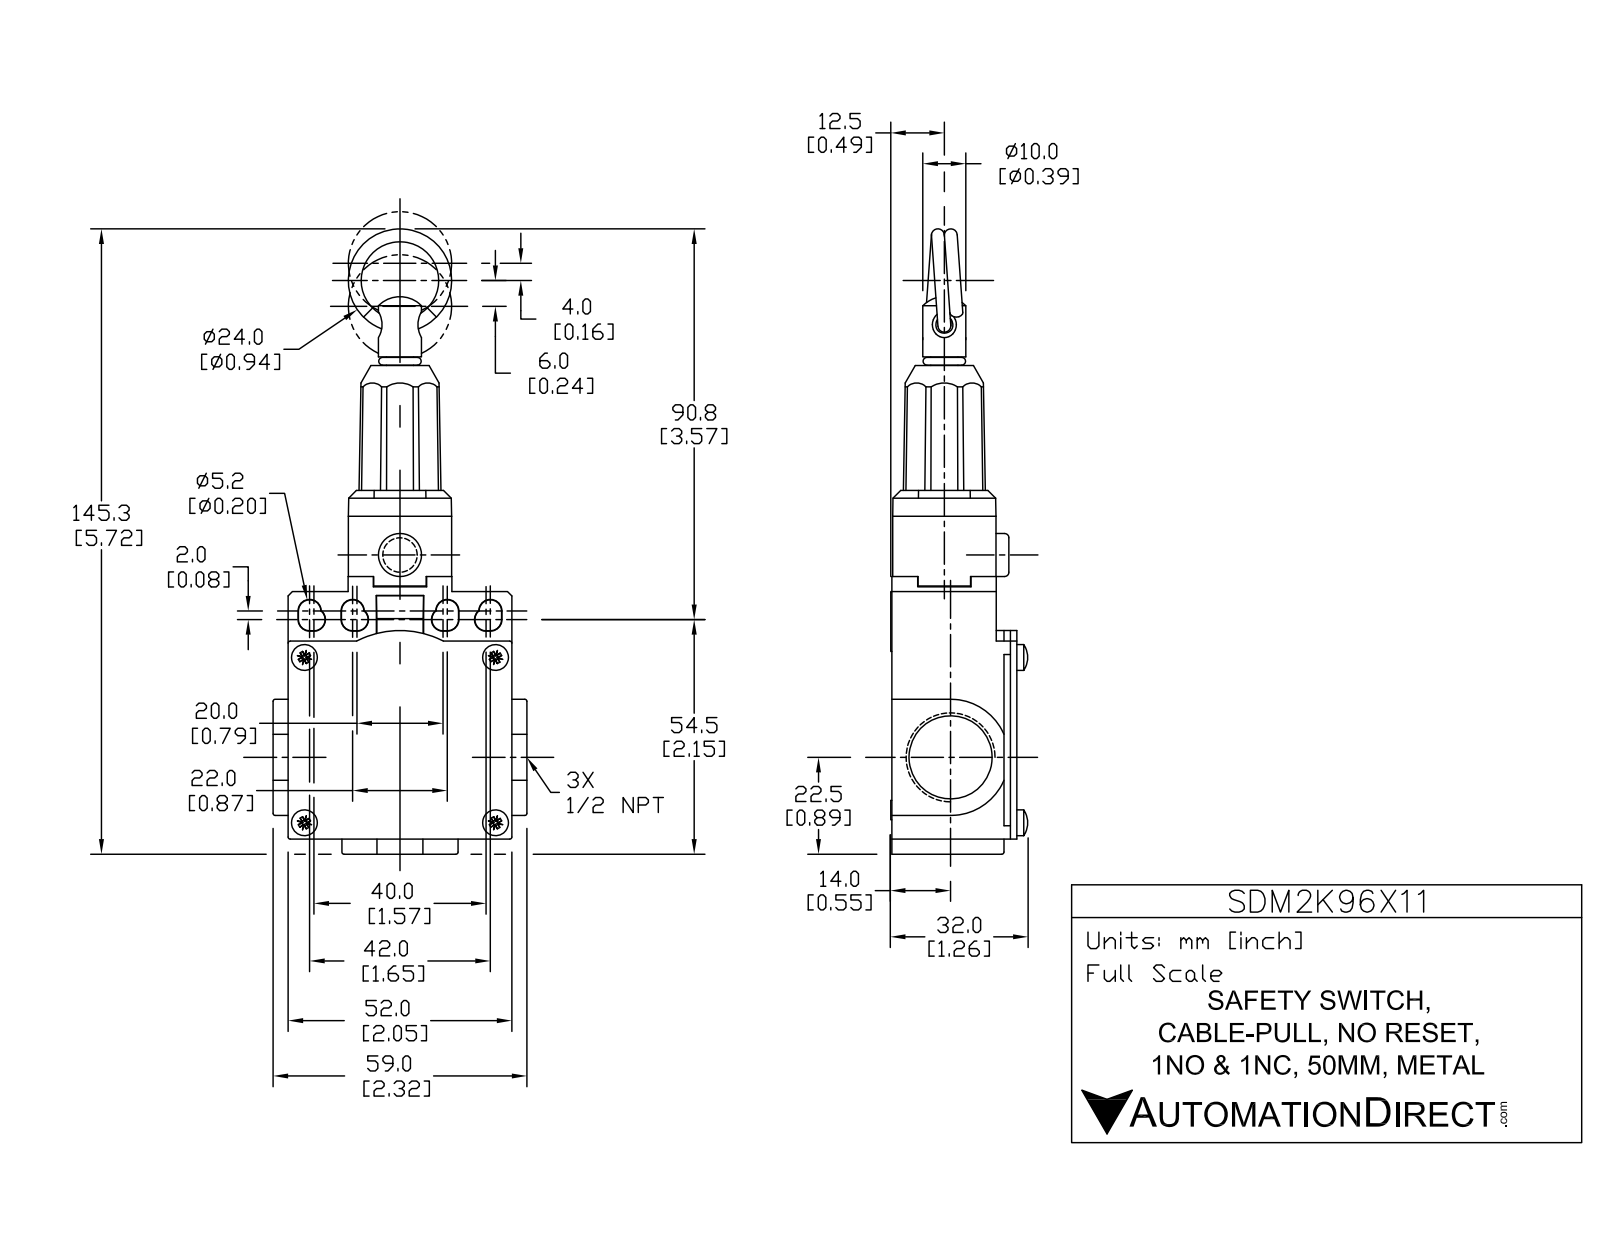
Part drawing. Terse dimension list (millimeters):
name: SDM2K96X11
written by: SolidWorks 2017 (AUTOMOTIVE_DESIGN)
unit: mm
bodies: 5 solids, 237 faces (109 planar, 95 cylindrical, 33 other)
size: 146.5 × 59 × 31.8
volume: 105 000 mm³; area: 25 530 mm²
holes: 2× ⌀17, 2× ⌀19, 1× ⌀4, 1× ⌀10.1, 1× ⌀15
bosses: 4× ⌀5.6, 4× ⌀5.5, 2× ⌀10, 1× ⌀6.3
rounds: 12× R2.6, 10× R0.5, 4× R3, 2× R13.5, 1× R10, 1× R10.2, 1× R22
face distances: 29.1, 3.5, 14, 24, 2.5, 38, 6, 52, 5.1, 35.5
hole spacings: 1.8, 101.5
